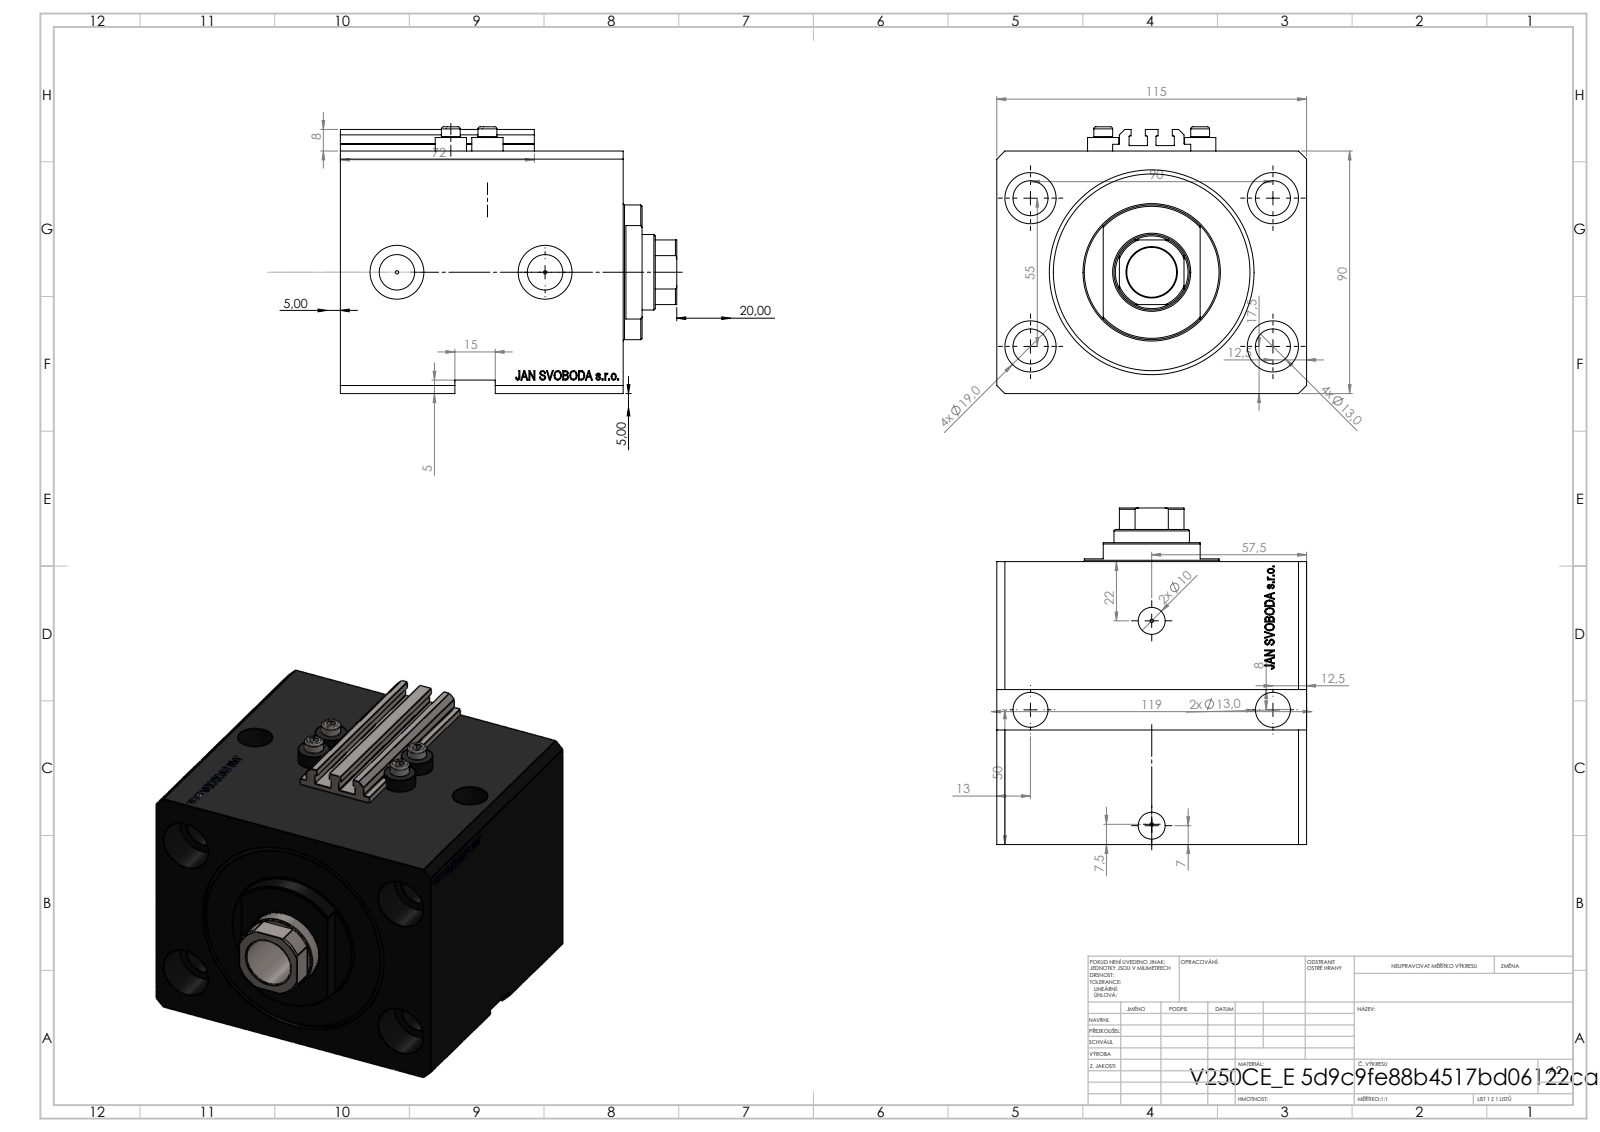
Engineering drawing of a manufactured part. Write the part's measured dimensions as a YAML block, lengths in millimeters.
part_name: "V250CE_VC_E; ALLEN BOLT V250CE; V250CE_E_Body; V250CE_C_VCP"
step_written_by: "SolidWorks 2019 (CONFIG_CONTROL_DESIGN)"
units: millimeters
bodies: {solids: 8, faces: 1107, planar: 543, cylindrical: 126, other: 438}
overall_size: [124.9, 115, 99]
volume: 954523
surface_area: 156491
round_holes:
  - {diameter: 13, count: 6}
  - {diameter: 1.25, count: 4}
  - {diameter: 4, count: 4}
  - {diameter: 19, count: 4}
  - {diameter: 10, count: 2}
  - {diameter: 13.16, count: 2}
  - {diameter: 20, count: 2}
  - {diameter: 18.5, count: 1}
  - {diameter: 28, count: 1}
  - {diameter: 63, count: 1}
  - {diameter: 76, count: 1}
round_bosses_or_shafts:
  - {diameter: 11.6, count: 4}
  - {diameter: 7, count: 4}
  - {diameter: 50, count: 1}
partial_cylinders:
  - {radius: 0.2, count: 10}
  - {radius: 13.5, count: 1}
face_to_face_distances: [90, 115, 105, 87.1, 17.9, 57, 74.9, 30.1, 20, 54.9]
hole_center_spacings: [52.74, 55, 90, 13.6, 27.39, 28.46, 33.62, 36]
